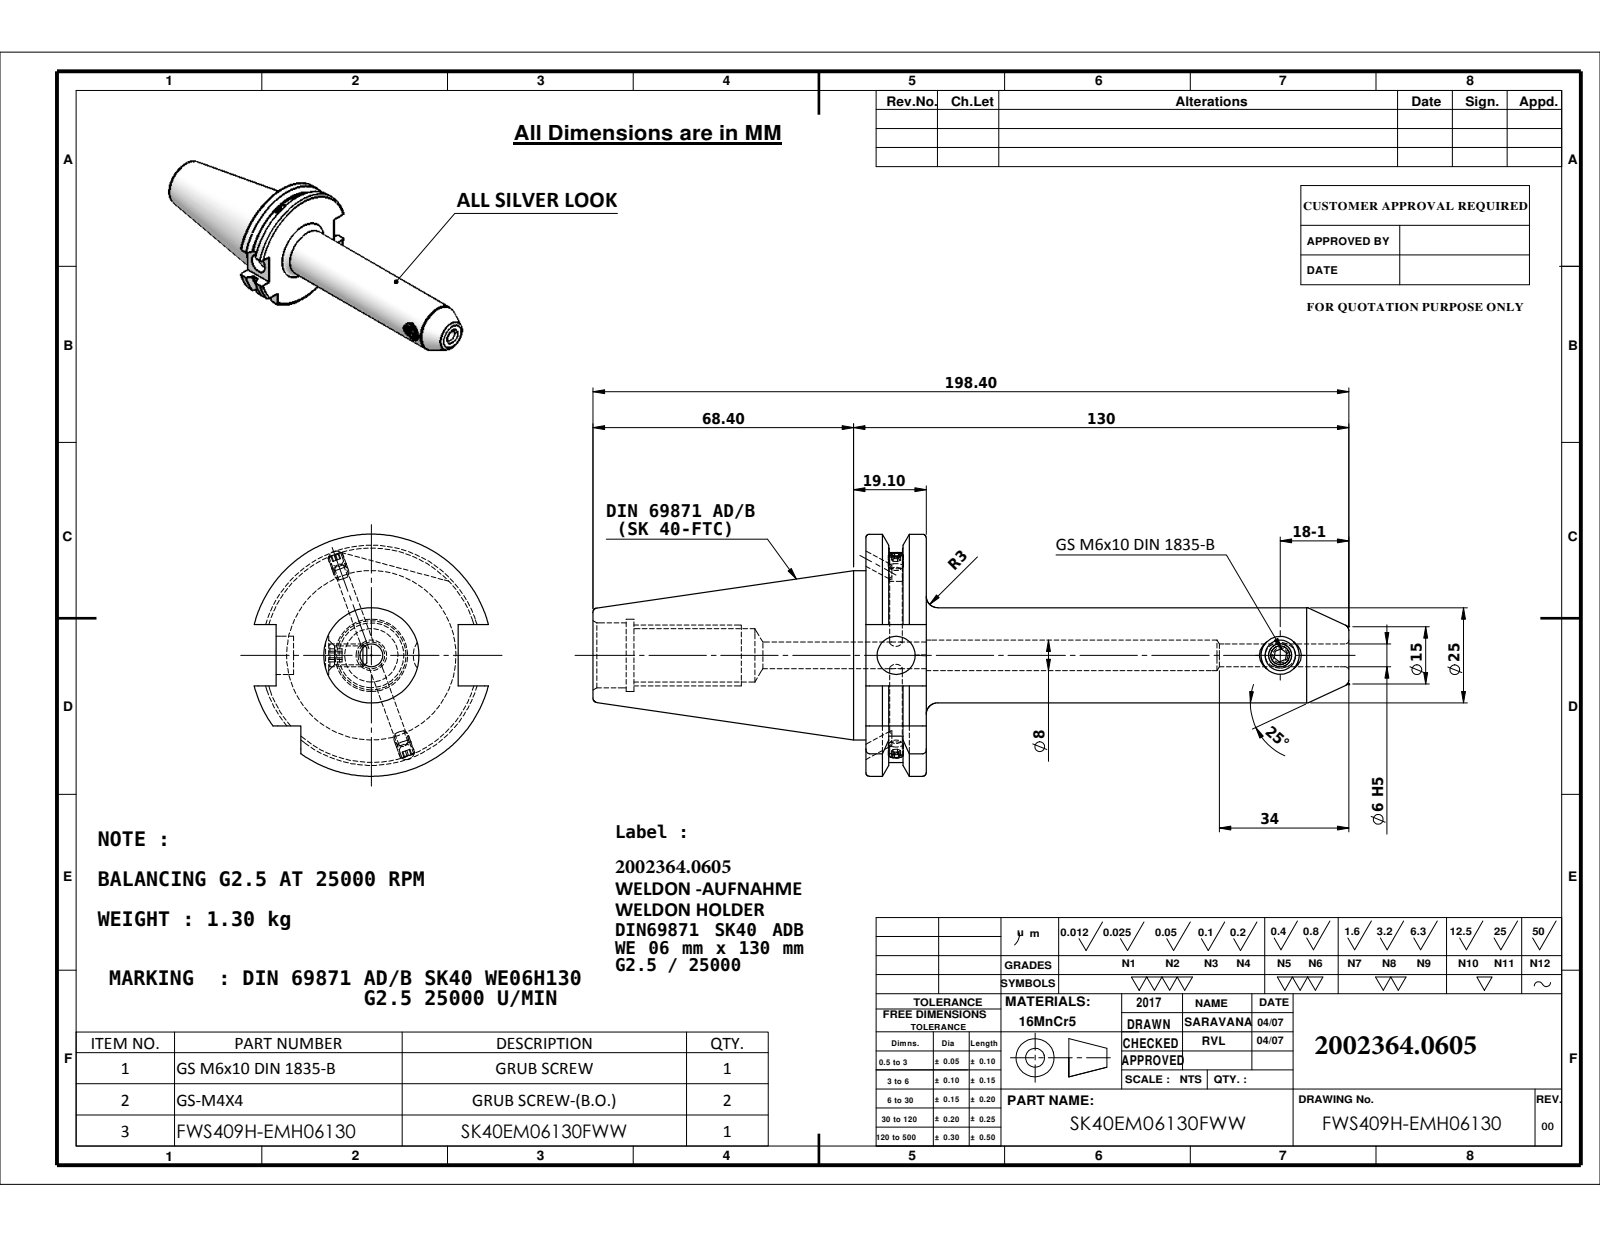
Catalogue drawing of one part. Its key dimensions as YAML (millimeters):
part_name: "M6X10_DIN 913 - M6 x 10-N; 91406-WE706130; M4X4_DIN 913 - M4 x 4-N; SK40EM06130FWW"
step_written_by: "SolidWorks 2009 (CONFIG_CONTROL_DESIGN)"
units: millimeters
bodies: {solids: 5, faces: 160, planar: 57, cylindrical: 42, other: 61}
overall_size: [198.4, 63.55, 61.48]
volume: 152195
surface_area: 31611
round_holes:
  - {diameter: 10, count: 2}
  - {diameter: 3.3, count: 1}
  - {diameter: 5, count: 1}
  - {diameter: 6, count: 1}
  - {diameter: 7, count: 1}
  - {diameter: 14, count: 1}
  - {diameter: 17, count: 1}
  - {diameter: 19, count: 1}
round_bosses_or_shafts:
  - {diameter: 4, count: 2}
  - {diameter: 44.45, count: 1}
  - {diameter: 25, count: 1}
  - {diameter: 6, count: 1}
partial_cylinders:
  - {radius: 28.12, count: 1}
  - {radius: 31.77, count: 1}
face_to_face_distances: [15.9, 16.1, 47.8, 71.6, 87.5, 10.7, 60.9, 76.8, 77.63, 66.93]
hole_center_spacings: [100.85]
